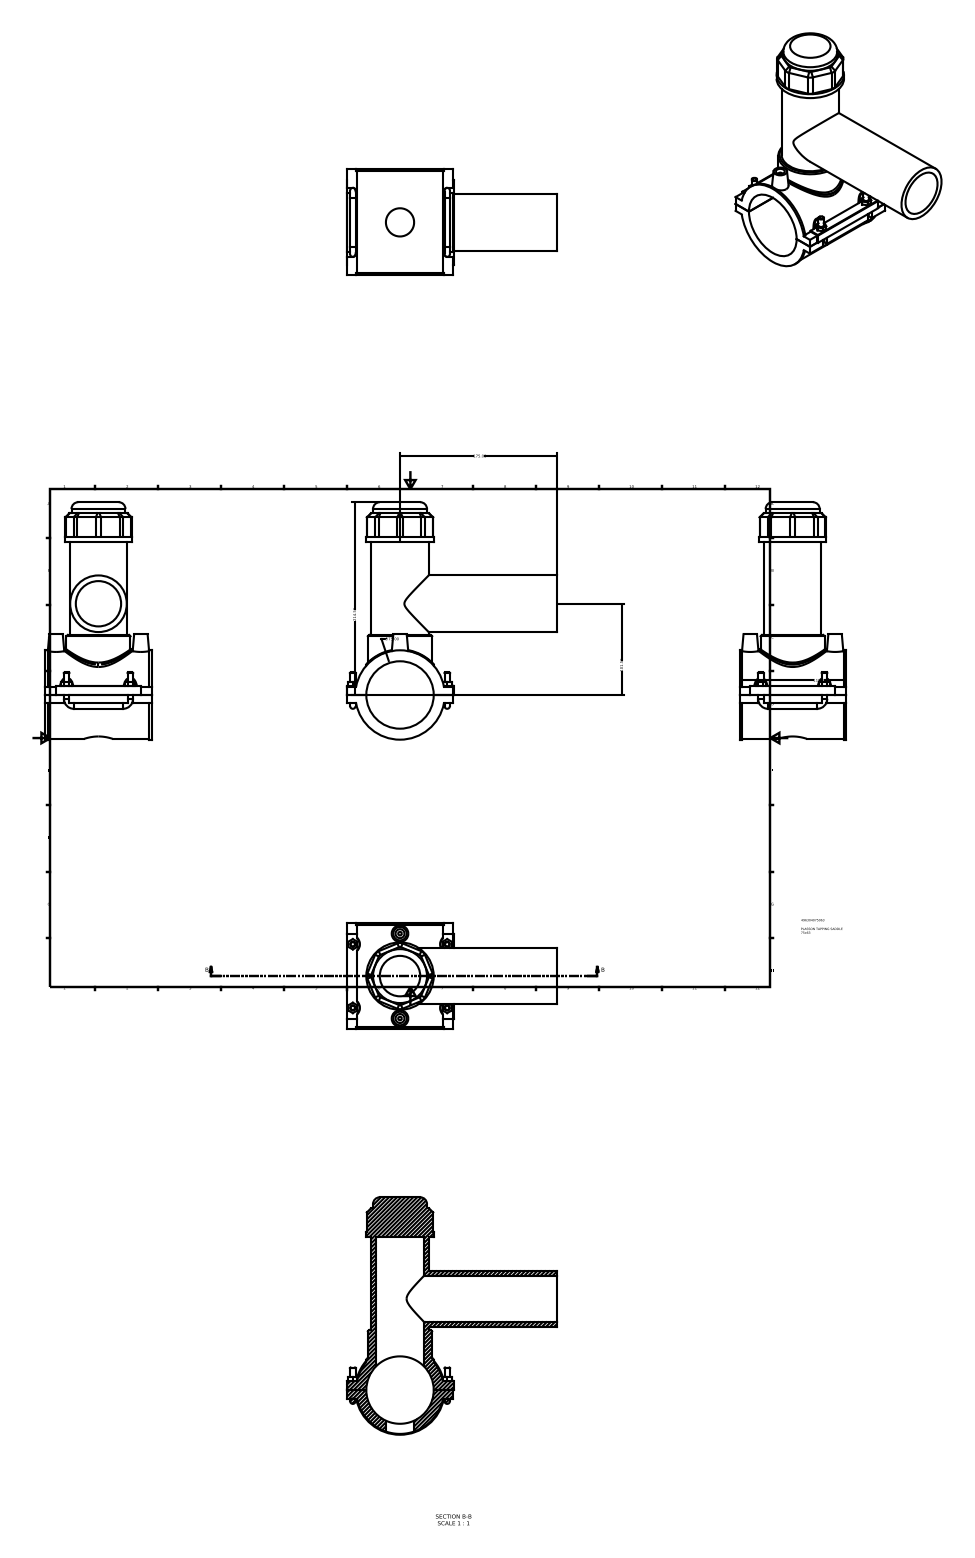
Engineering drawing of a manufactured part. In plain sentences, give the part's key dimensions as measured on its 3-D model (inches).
The part is named "496304075063". Its 3-D file was written by "Autodesk Inventor 2015 (AUTOMOTIVE_DESIGN)". It is 1 solid with 185 faces: 111 planar, 49 cylindrical and 25 other. Overall it measures 10.403 by 9.232 by 4.646 inches. Its volume is 52 cubic inches and its surface area 315.7 square inches. Round holes: 2 of diameter 0.394, 1 of diameter 1.235, 1 of diameter 1.984, 1 of diameter 2.067, 1 of diameter 2.953. Round bosses or shafts: 6 of diameter 0.236, 2 of diameter 0.157, 1 of diameter 3.915, 1 of diameter 3.839, 1 of diameter 2.953, 1 of diameter 2.805, 1 of diameter 2.51, 1 of diameter 2.48. Partial cylindrical surfaces (rounded edges, fillets, slot ends): 12 of radius 0.295, 4 of radius 0.118, 1 of radius 0.02, 1 of radius 1.996. The main face-to-face distances are 4.646, 6.705, 6.701, 0.367, 0.371, 0.039, 7.072, 0.778, 0.411, 0.407. The hole center spacings are 1.858, 3.717.
